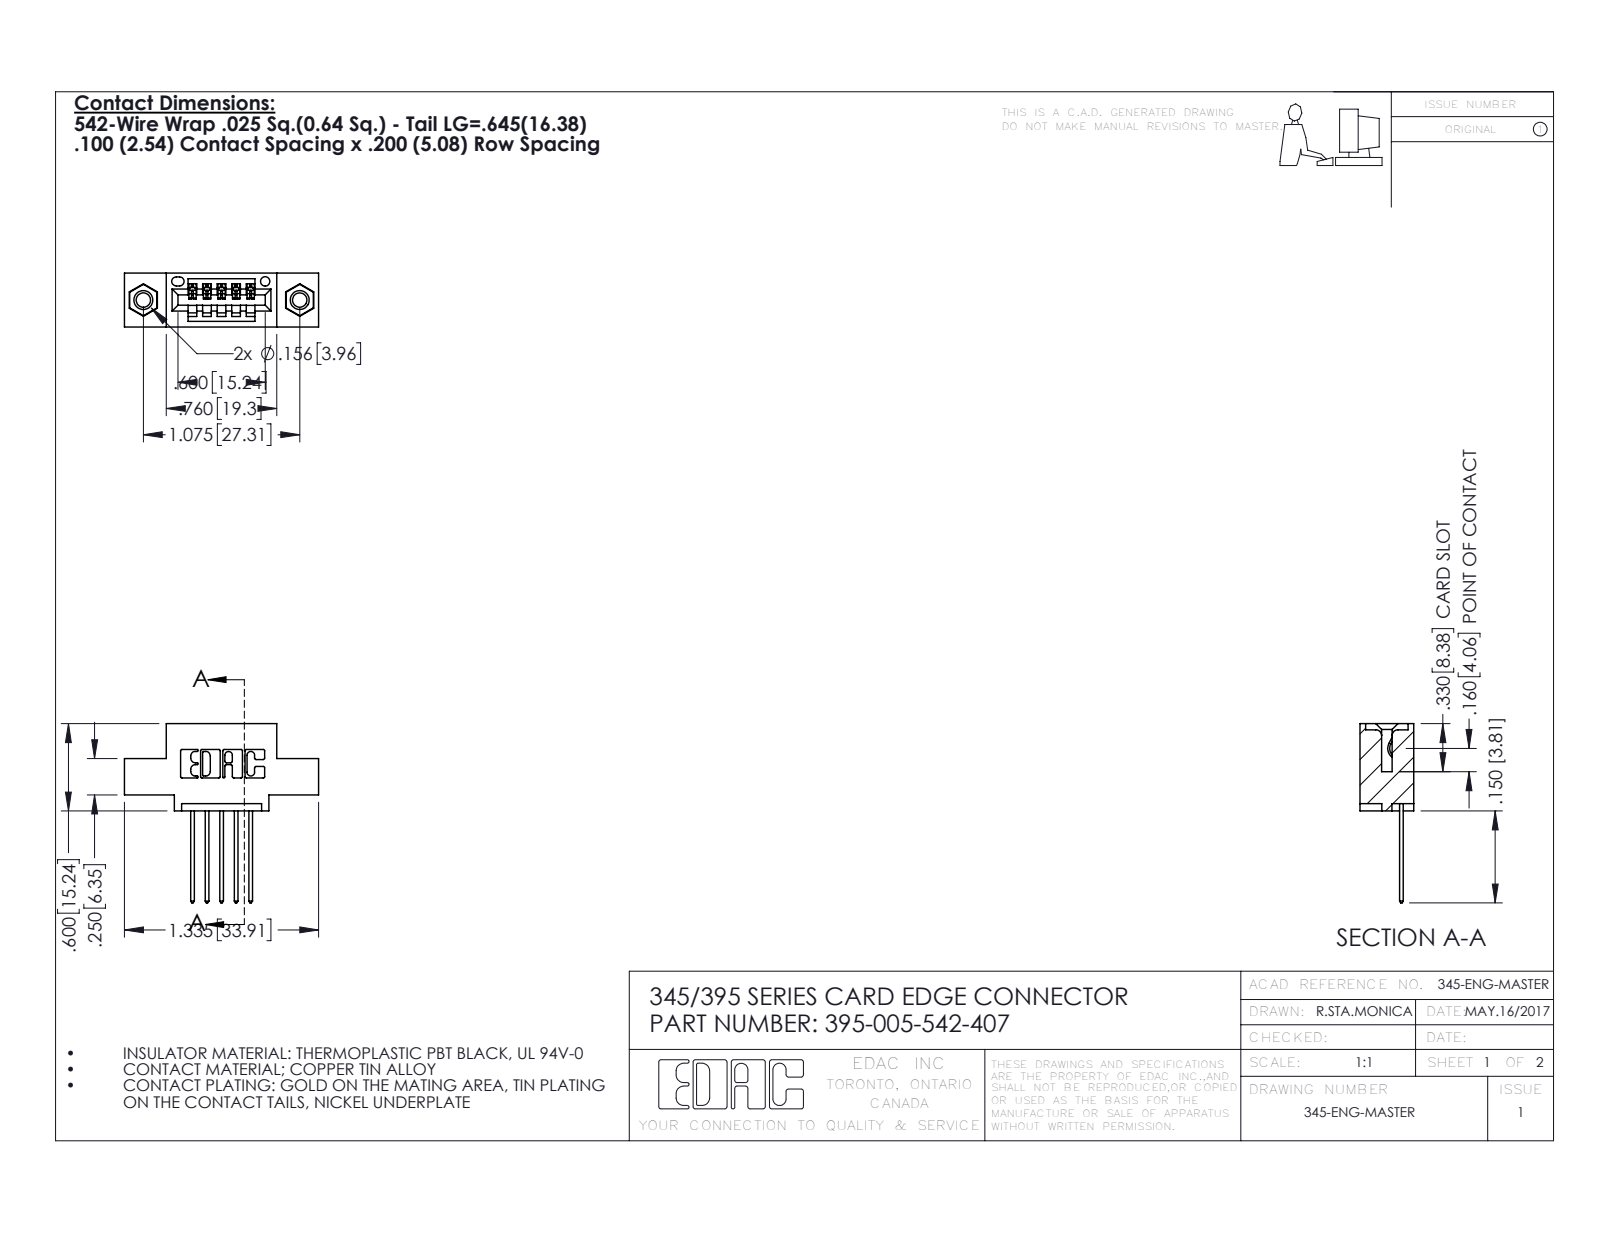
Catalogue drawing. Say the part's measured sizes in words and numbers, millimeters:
The part is named "345 Part_0.110 Offset - 0.156 Dia-TI; 395-005-542-407; 345-250-001_345-250-005-103; 345-292-001_345-293-142". Its 3-D file was written by "SolidWorks 2016 (CONFIG_CONTROL_DESIGN)". It is 8 solids with 480 faces: 316 planar, 148 cylindrical and 16 other. Overall it measures 33.9 by 31.3 by 9.4 millimeters. Its volume is 2 830 cubic millimeters and its surface area 3 459 square millimeters. Round holes: 2 of diameter 2.5, 2 of diameter 3.2, 2 of diameter 4, 1 of diameter 1.6. Round bosses or shafts: 2 of diameter 3.9. Partial cylindrical surfaces (rounded edges, fillets, slot ends): 22 of radius 0.3, 10 of radius 0.2, 10 of radius 0.3, 6 of radius 0.2, 6 of radius 0.8, 3 of radius 0.7, 2 of radius 0.8, 2 of radius 1. The main face-to-face distances are 5.1, 9.4, 1.8, 7.6, 2.5, 0.6, 2.5, 6.9, 6.4, 1.5. The hole center spacings are 6.9, 21.5, 27.3.
